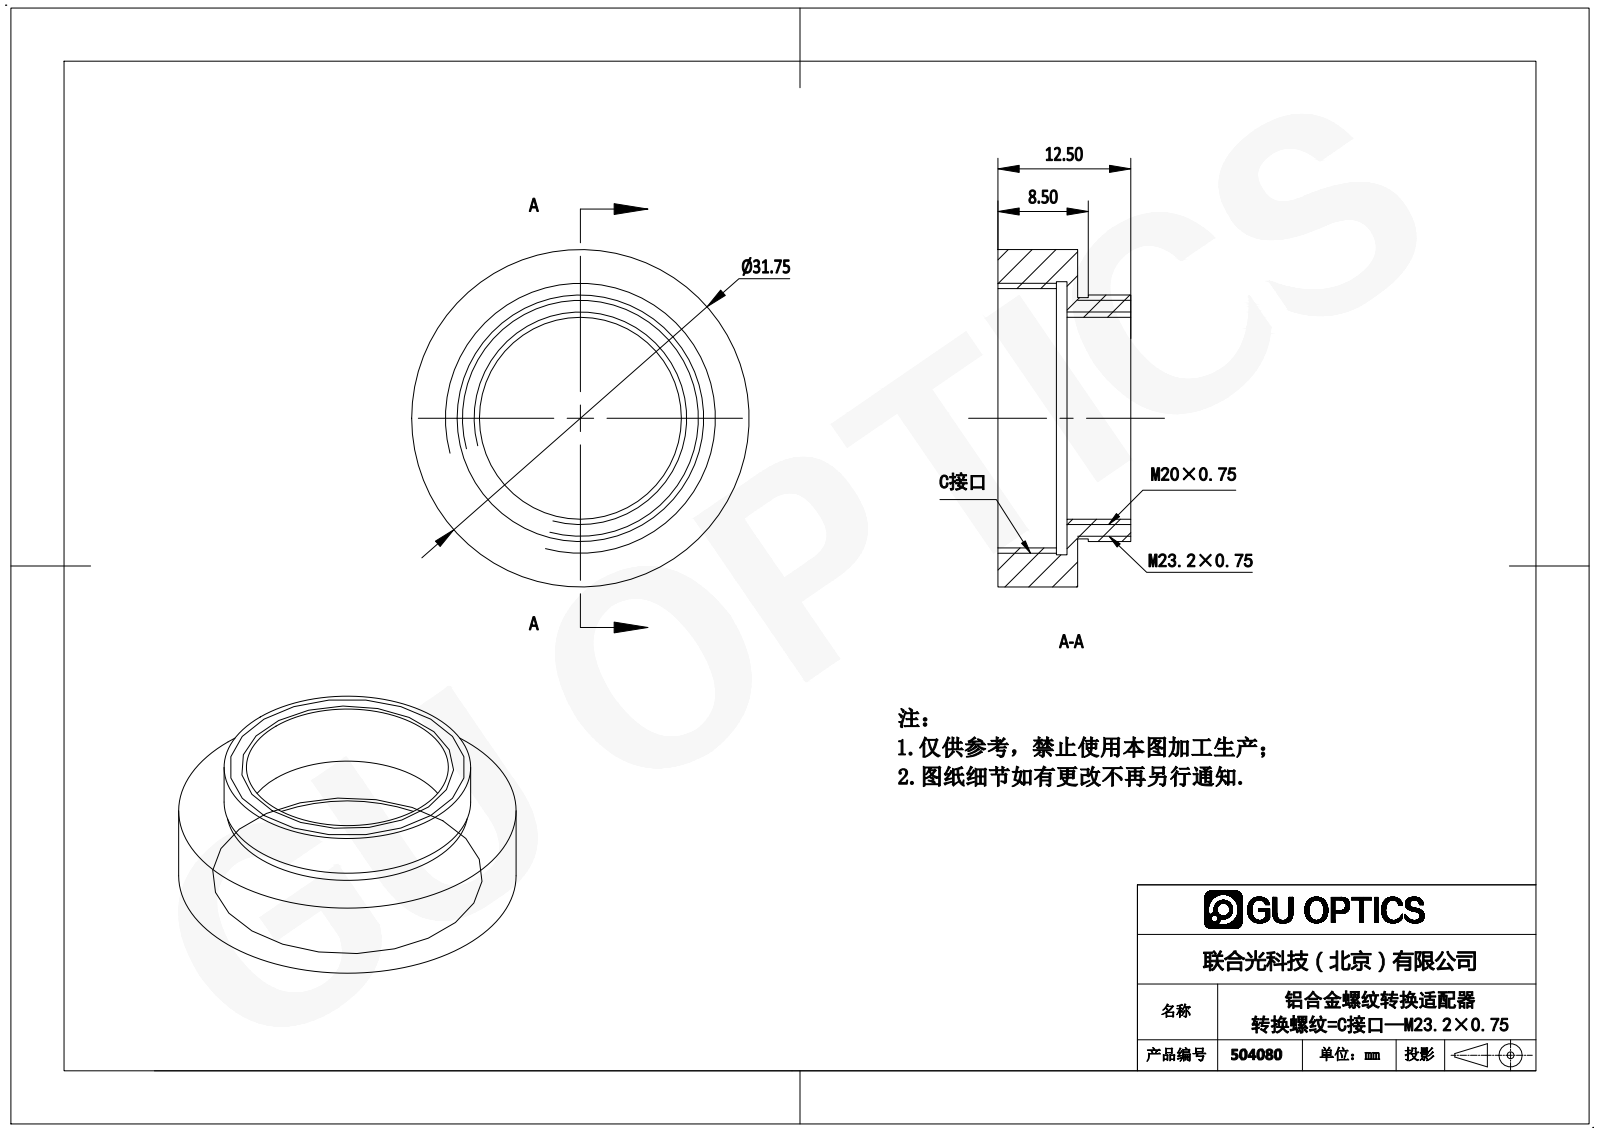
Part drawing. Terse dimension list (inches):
name: 504080
written by: SolidWorks 2016 (AUTOMOTIVE_DESIGN)
unit: in
bodies: 1 solid, 18 faces (6 planar, 12 cylindrical, 0 other)
size: 1.25 × 1.25 × 0.492
volume: 0.198 in³; area: 4.845 in²
holes: 1× ⌀0.748, 1× ⌀0.961, 1× ⌀1.012
bosses: 1× ⌀1.25, 1× ⌀0.913, 1× ⌀0.894
face distances: 0.295, 0.039, 0.256, 0.492, 0.236, 0.197, 0.079, 0.217, 0.276, 0.335
